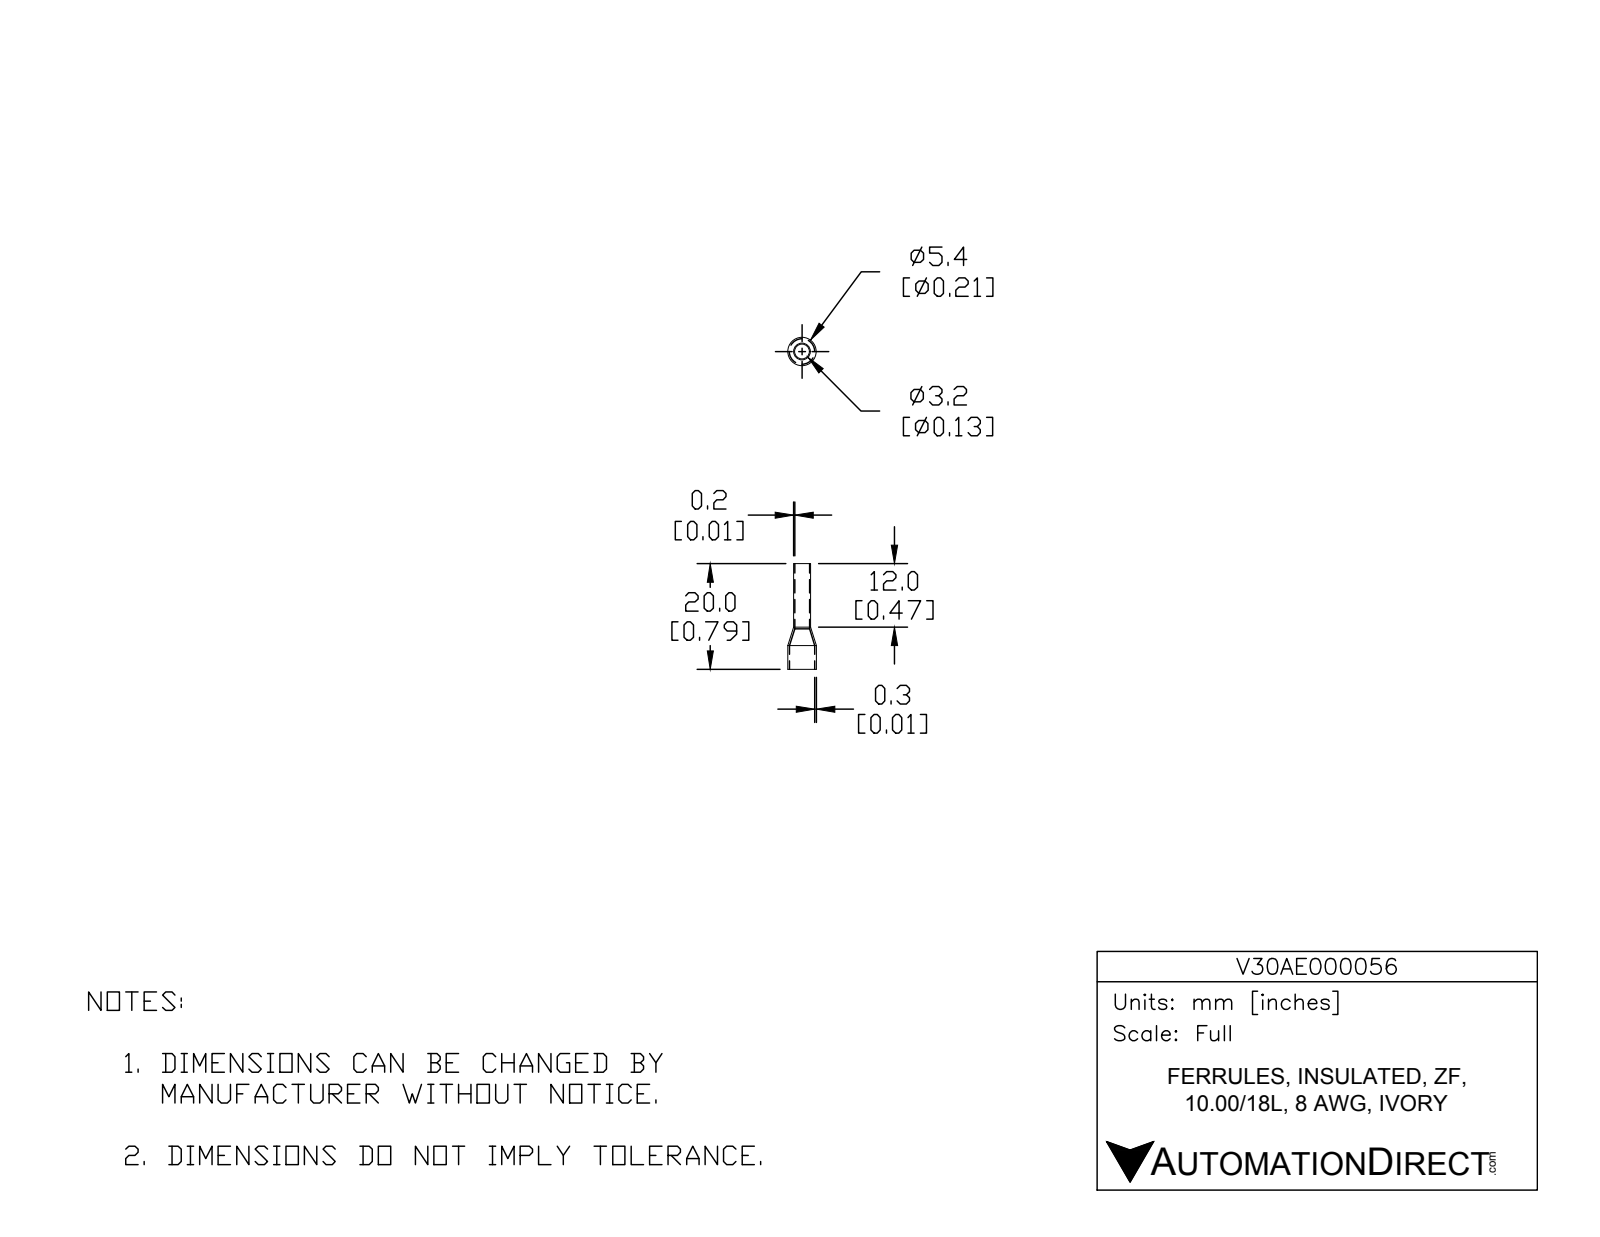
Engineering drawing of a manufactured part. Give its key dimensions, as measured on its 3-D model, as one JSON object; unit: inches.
{"part_name": "V30AE000056", "step_written_by": "SolidWorks 2017 (AUTOMOTIVE_DESIGN)", "units": "inches", "bodies": {"solids": 1, "faces": 14, "planar": 2, "cylindrical": 8, "other": 4}, "overall_size": [0.787, 0.213, 0.213], "volume_in3": 0.003, "surface_area_in2": 0.727, "round_holes": [[0.11, 1], [0.189, 1]], "round_bosses_or_shafts": [[0.213, 1], [0.126, 1]], "face_to_face_distances": [0.787]}
